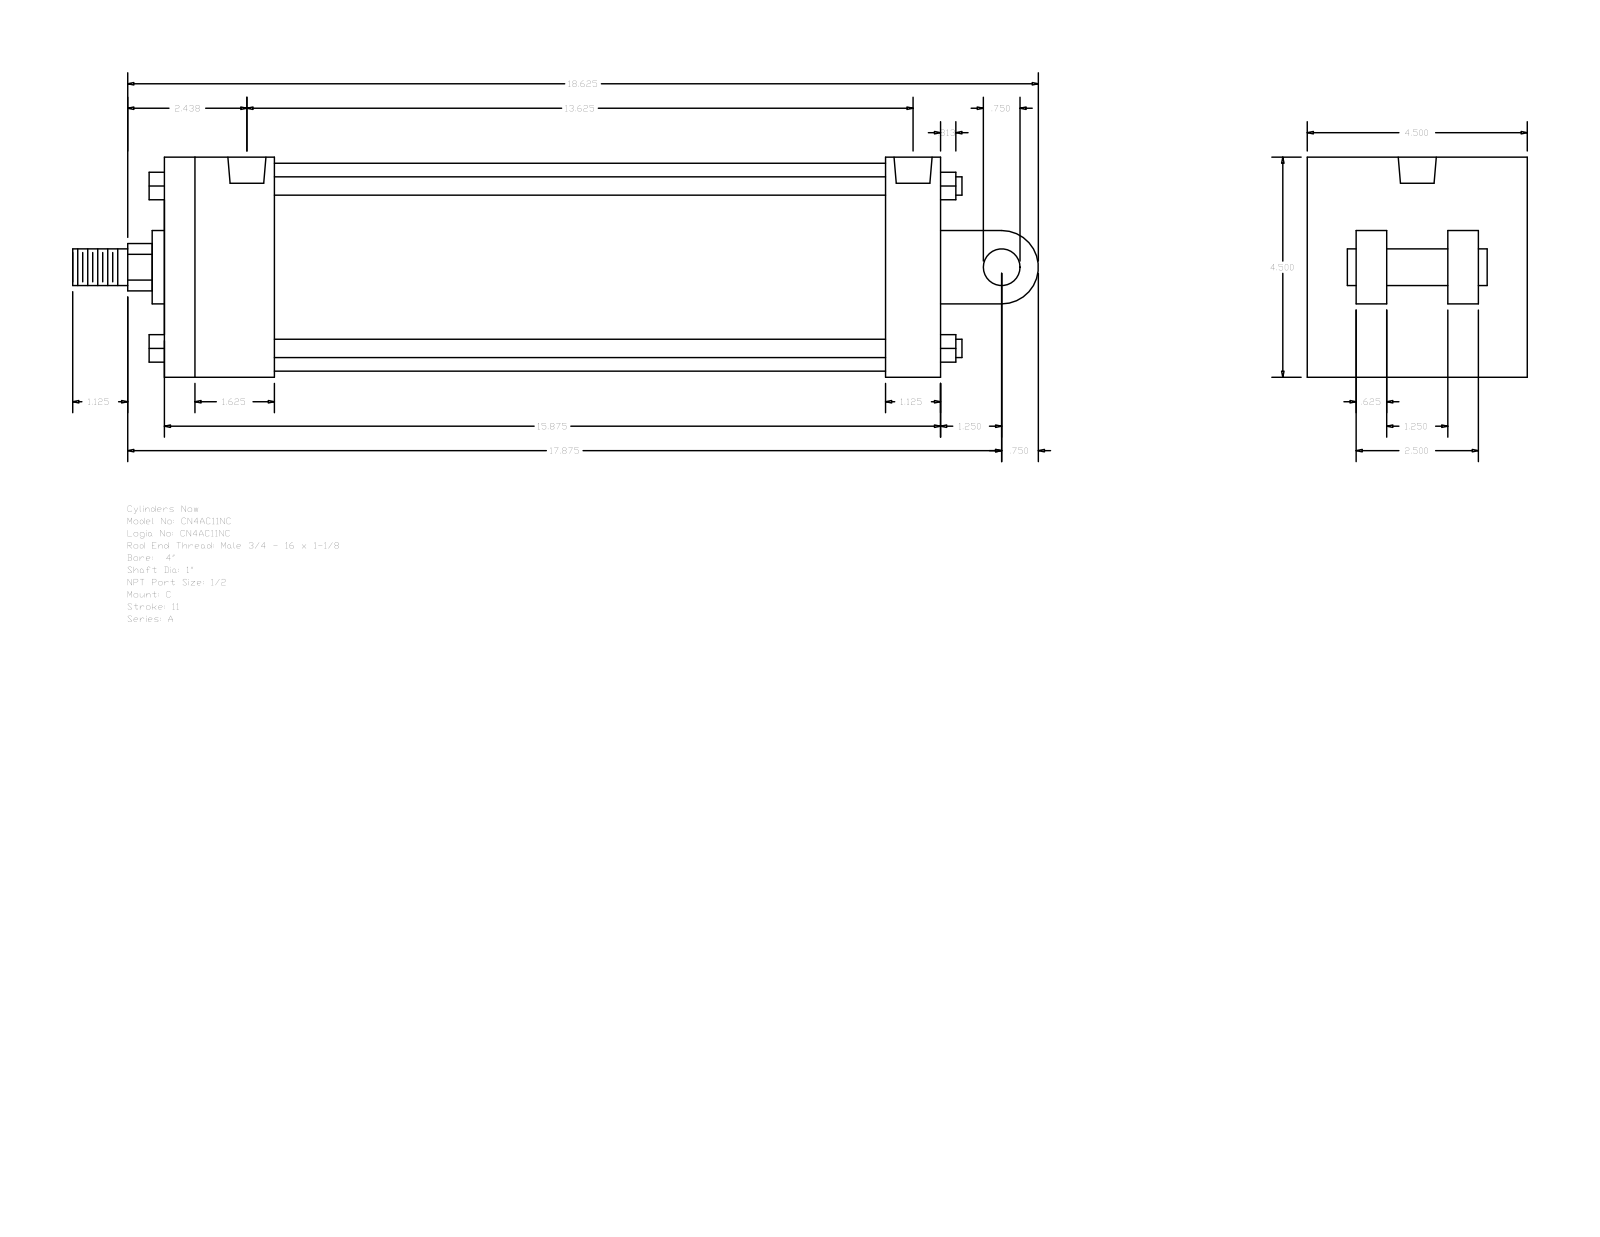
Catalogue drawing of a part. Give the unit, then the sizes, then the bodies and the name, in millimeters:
Units: millimetres
Overall size (bounding box): 501.65 × 114.3 × 114.3
Round holes (diameter × count): ⌀8.73 ×4, ⌀19.77 ×2
Round bosses / shafts (diameter × count): ⌀9.53 ×4, ⌀19.05 ×2, ⌀107.95 ×1, ⌀38.1 ×1, ⌀25.4 ×1
Partial cylindrical surfaces — rounded edges, fillets, slot ends (radius × count): R12.29 ×1, R19.05 ×1
Main face-to-face distances: 114.3, 403.22, 73.03, 28.57, 374.65, 57.15, 317.5, 346.07, 41.27, 38.1
Hole centre spacings: 3.18, 339.72, 342.9, 346.08
Bodies: 0 solids, 135 faces (102 planar, 33 cylindrical, 0 other)
Part name (STEP PRODUCT): A_C__0400_1
STEP written by: GSSL Pune (CONFIG_CONTROL_DESIGN)
